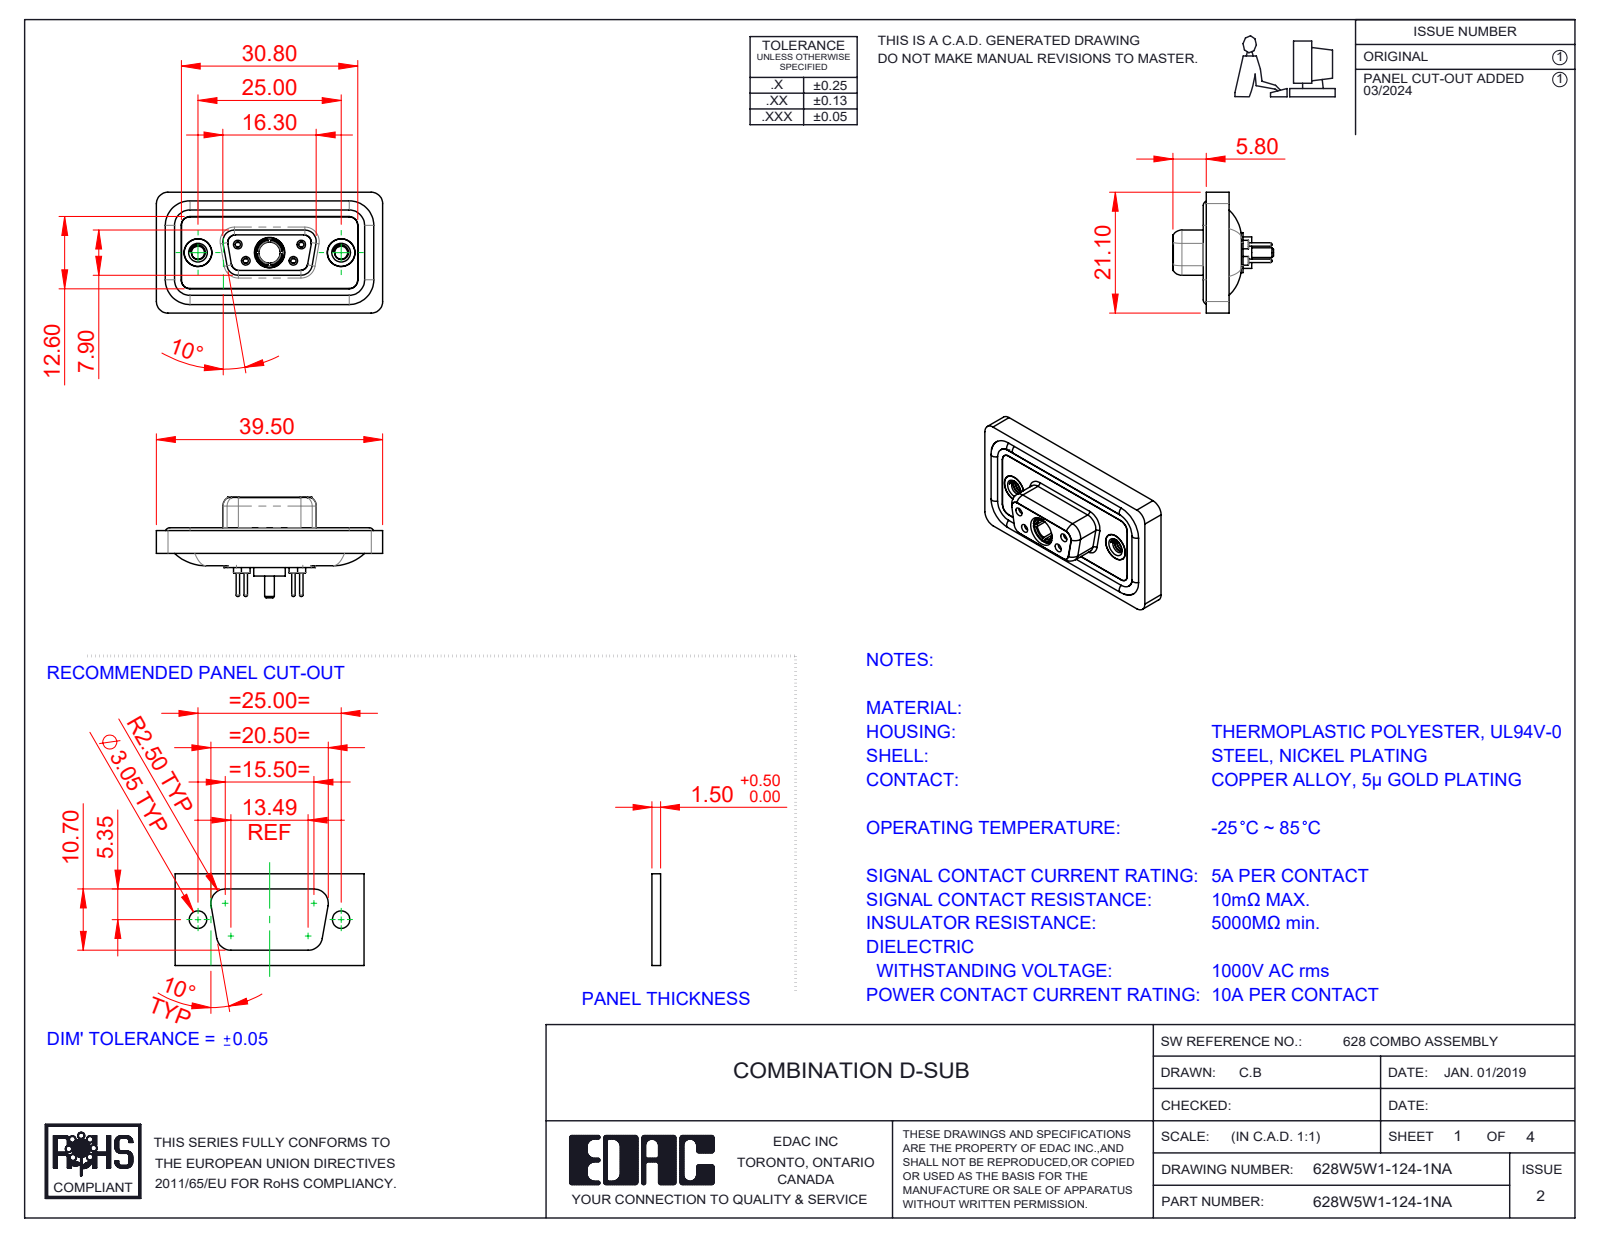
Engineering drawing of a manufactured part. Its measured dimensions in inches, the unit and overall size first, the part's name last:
Units: inches
Overall size (bounding box): 1.555 × 0.831 × 0.691
Round holes (diameter × count): ⌀0.035 ×4, ⌀0.043 ×4, ⌀0.059 ×4, ⌀0.079 ×4, ⌀0.191 ×3, ⌀0.063 ×2, ⌀0.067 ×2, ⌀0.089 ×2, ⌀0.157 ×2, ⌀0.159 ×2, ⌀0.197 ×2, ⌀0.146 ×1
Round bosses / shafts (diameter × count): ⌀0.063 ×6, ⌀0.087 ×4, ⌀0.024 ×4, ⌀0.195 ×2, ⌀0.189 ×2, ⌀0.217 ×1, ⌀0.205 ×1, ⌀0.195 ×1
Partial cylindrical surfaces — rounded edges, fillets, slot ends (radius × count): R0.059 ×22, R0.079 ×18, R0.053 ×8, R0.063 ×8, R0.01 ×4, R0.02 ×4, R0.024 ×4, R0.026 ×4
Main face-to-face distances: 0.016, 0.114, 0.071, 0.043, 0.063, 0.02, 0.222, 0.293, 0.211, 0.26
Hole centre spacings: 0.124, 0.225, 0.28, 0.492, 0.713, 0.173, 0.173, 0.327
Volume: 0.29 in³ · Surface area: 11.81 in²
Bodies: 13 solids, 678 faces (194 planar, 289 cylindrical, 195 other)
Part name (STEP PRODUCT): 628Combo Housing_5W1; 628Combo Shell Front_09 Contacts; 628Combo Contact Row 2_24; 628Combo Contact Row 1_24 (+5 more)
STEP written by: SolidWorks 2023 (CONFIG_CONTROL_DESIGN)
